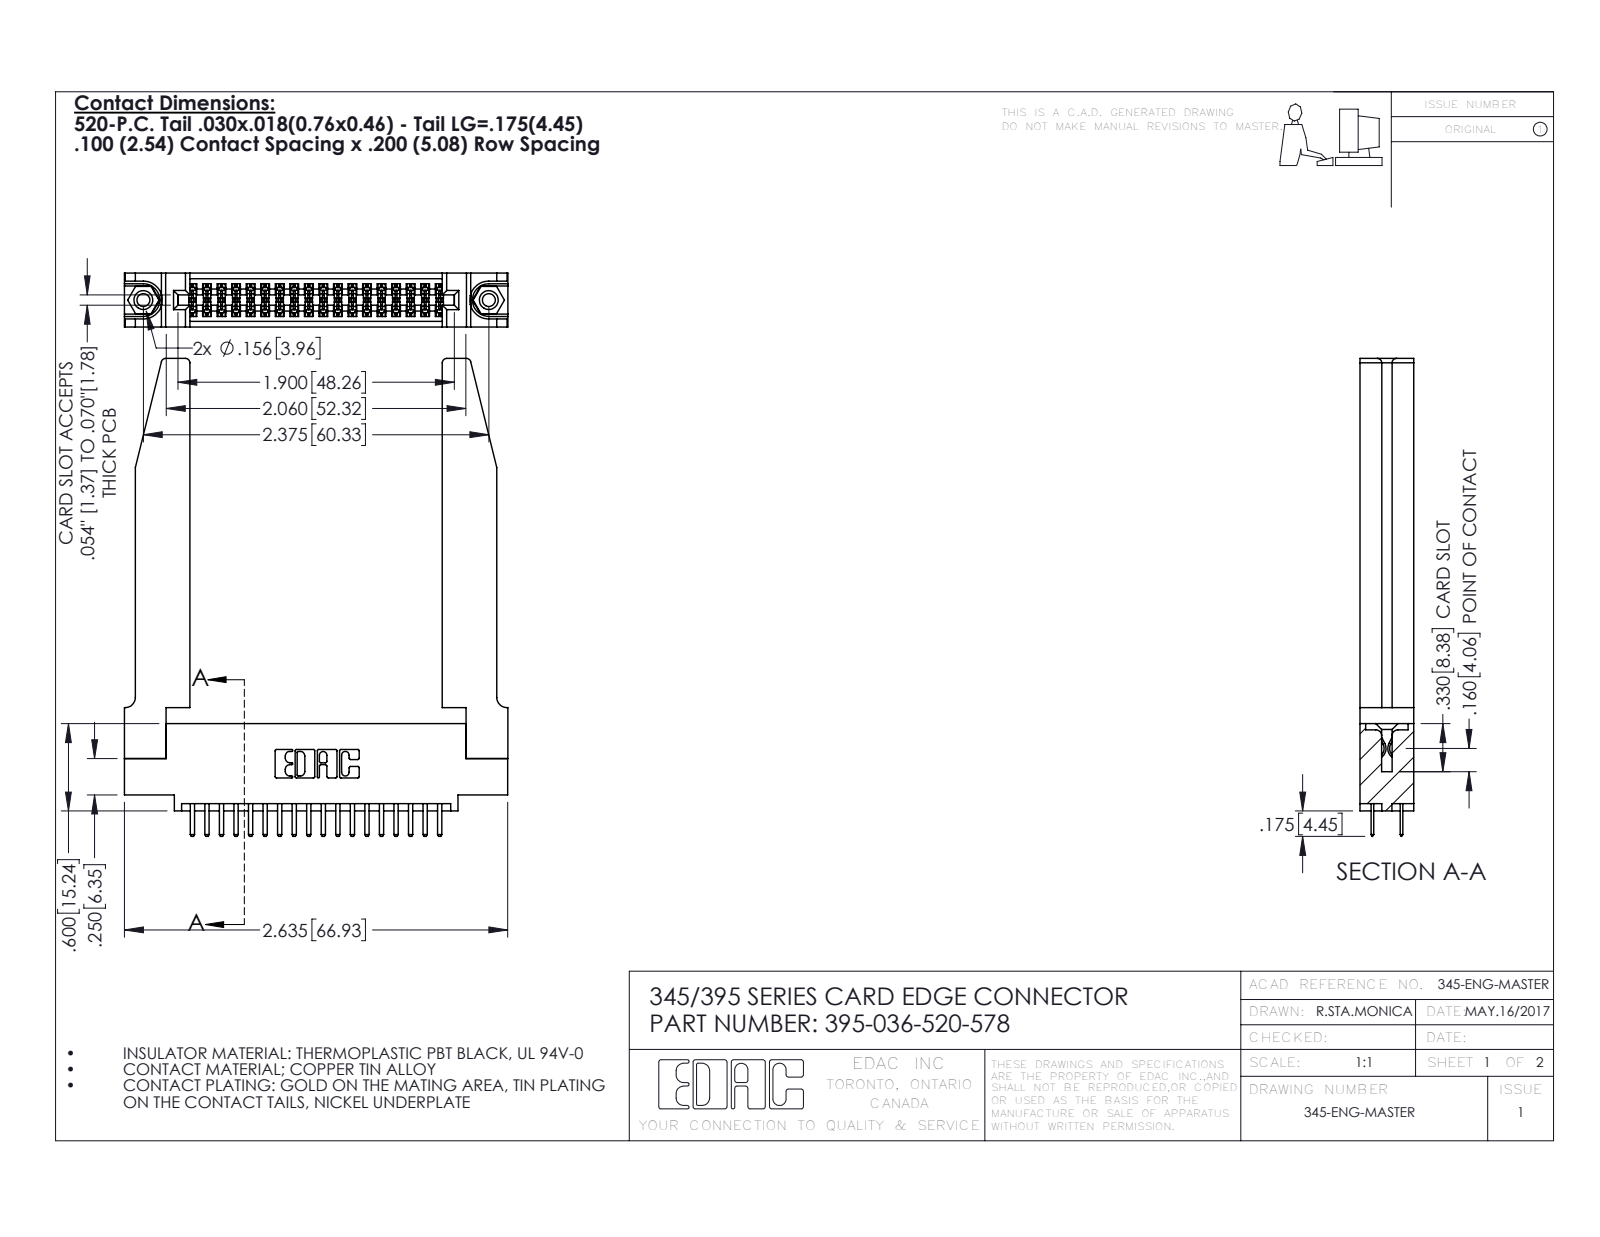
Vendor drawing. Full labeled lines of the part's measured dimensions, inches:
Part name (STEP PRODUCT): 345 Part_0.110 Offset - 0.156 Dia-TH; 345-220-078_345-220-078; 395-036-520-578; 345-292-001_345-293-120 (+1 more)
STEP written by: SolidWorks 2016 (CONFIG_CONTROL_DESIGN)
Units: inches
Bodies: 41 solids, 2308 faces (1486 planar, 770 cylindrical, 52 other)
Overall size (bounding box): 3.285 × 2.636 × 0.37
Volume: 0.852 in³ · Surface area: 24.16 in²
Round holes (diameter × count): ⌀0.089 ×2, ⌀0.125 ×2, ⌀0.156 ×2, ⌀0.064 ×1
Round bosses / shafts (diameter × count): ⌀0.155 ×2
Partial cylindrical surfaces — rounded edges, fillets, slot ends (radius × count): R0.006 ×54, R0.01 ×40, R0.01 ×22, R0.03 ×8, R0.007 ×6, R0.031 ×6, R0.026 ×3, R0.014 ×2
Main face-to-face distances: 0.37, 0.072, 0.298, 0.2, 0.098, 0.272, 0.025, 0.225, 0.15, 0.22
Hole centre spacings: 0.27, 2.141, 2.375
